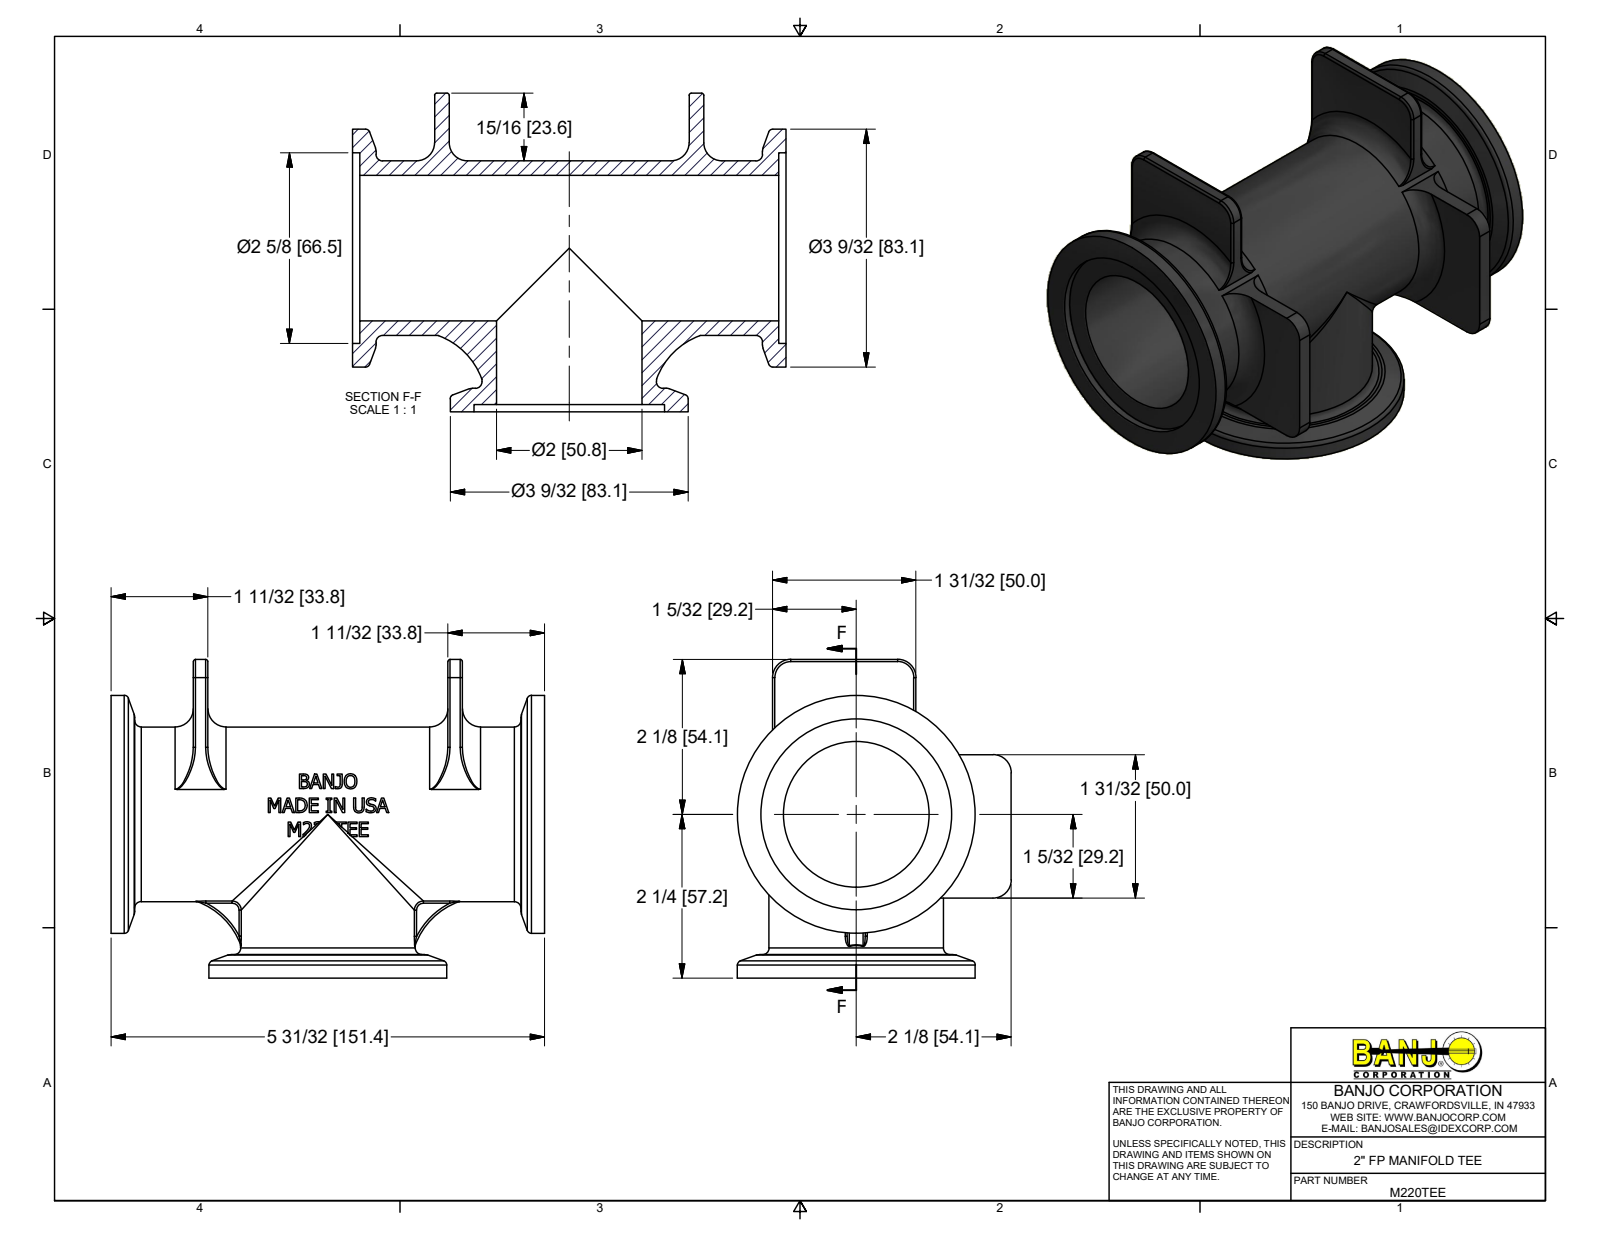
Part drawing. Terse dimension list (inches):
name: M220TEE
written by: Autodesk Inventor 2018 (AUTOMOTIVE_DESIGN)
unit: in
bodies: 1 solid, 420 faces (206 planar, 68 cylindrical, 146 other)
size: 5.96 × 4.38 × 3.765
volume: 14.16 in³; area: 138.6 in²
holes: 2× ⌀2, 2× ⌀2.62
bosses: 2× ⌀3.27, 2× ⌀2.4
rounds: 18× R0.03, 4× R0.25, 2× R1, 1× R1.23
face distances: 0.1, 0.2, 3.5, 1.13, 1.33, 4.63, 4.83, 1.23, 5.86, 1.03
